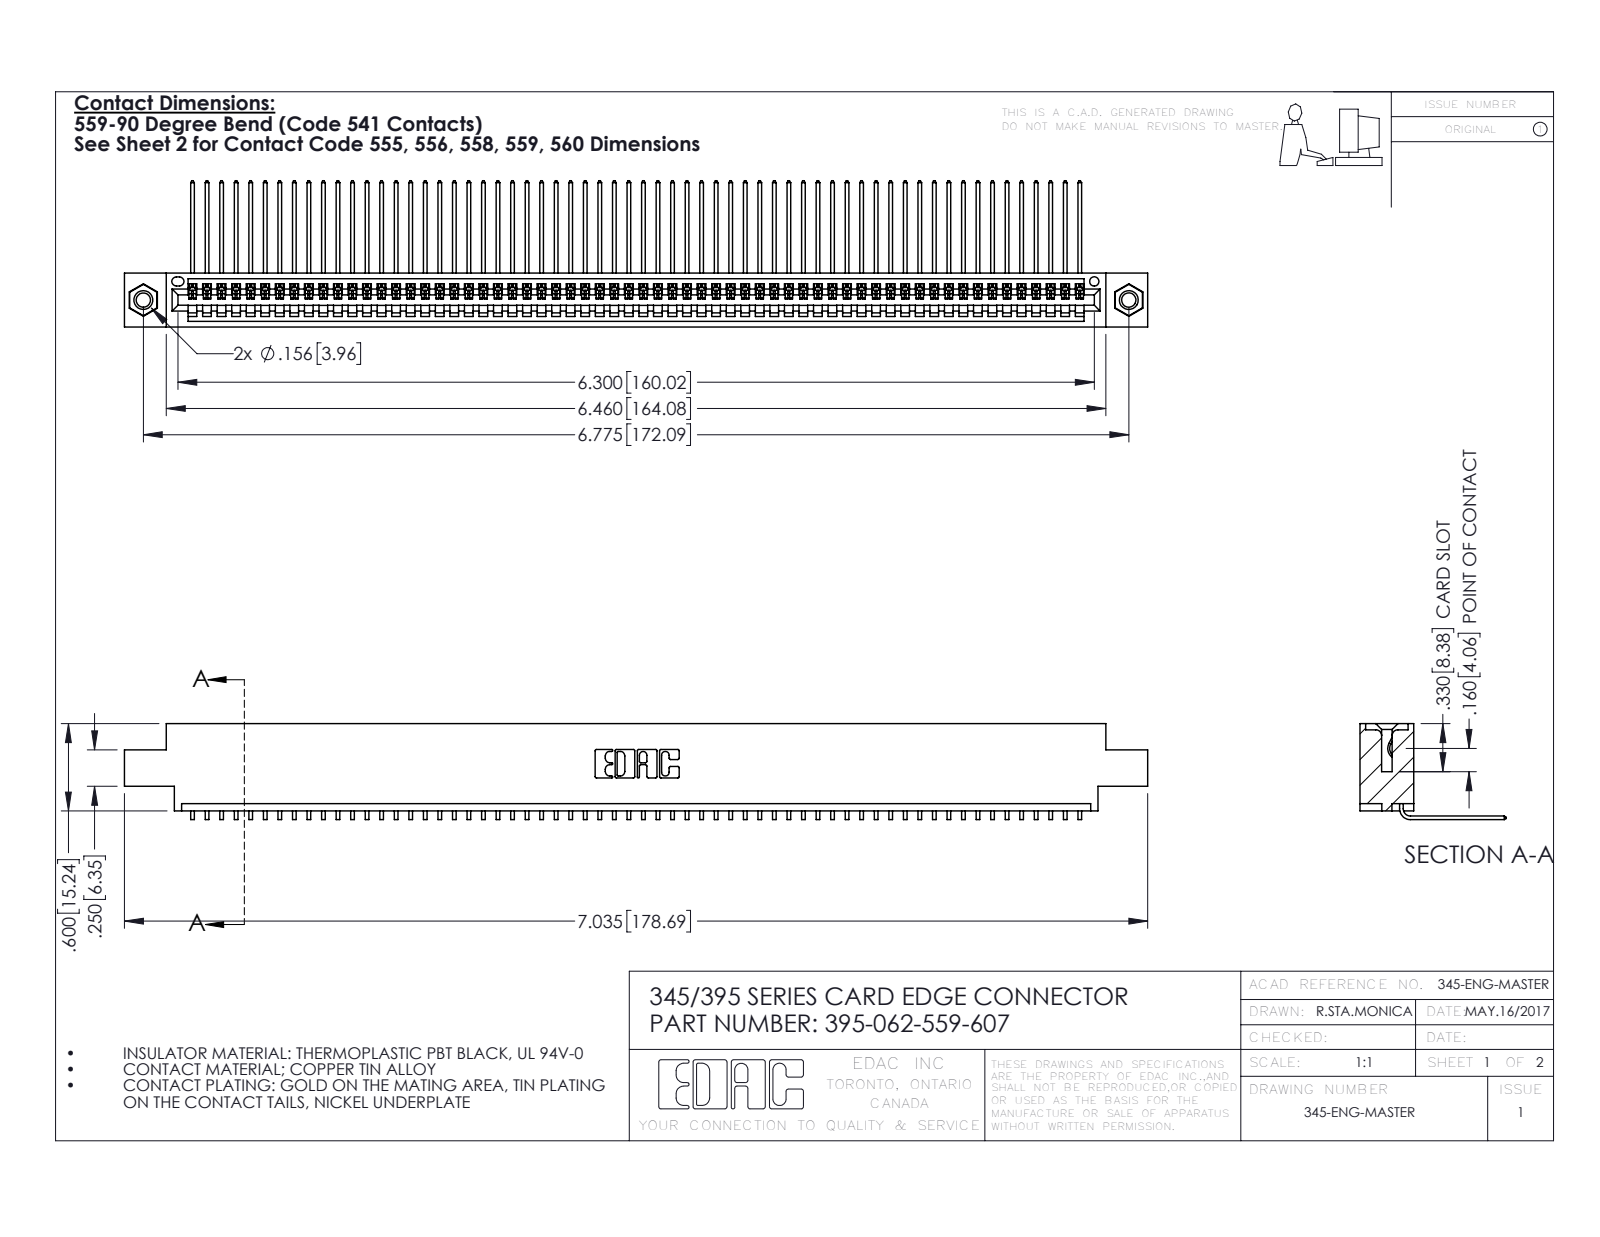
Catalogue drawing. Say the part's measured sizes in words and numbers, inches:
The part is named "395-062-559-607; 345 Part_0.170 Offset - 0.156 Dia-TI; 345-250-001_345-250-005-103; 345-292-001_558 559 Tail - 1". Its 3-D file was written by "SolidWorks 2016 (CONFIG_CONTROL_DESIGN)". It is 65 solids with 3910 faces: 2720 planar, 1174 cylindrical and 16 other. Overall it measures 7.035 by 1.005 by 0.659 inches. Its volume is 1.051 cubic inches and its surface area 38.01 square inches. Round holes: 2 of diameter 0.098, 2 of diameter 0.125, 2 of diameter 0.156, 1 of diameter 0.064. Round bosses or shafts: 2 of diameter 0.155. Partial cylindrical surfaces (rounded edges, fillets, slot ends): 124 of radius 0.006, 22 of radius 0.01, 6 of radius 0.007, 6 of radius 0.031, 3 of radius 0.026, 2 of radius 0.031, 2 of radius 0.04, 1 of radius 0.014. The main face-to-face distances are 0.072, 0.298, 0.37, 0.2, 0.098, 0.272, 0.025, 0.225, 0.175, 0.149. The hole center spacings are 0.27, 6.539, 6.775.
